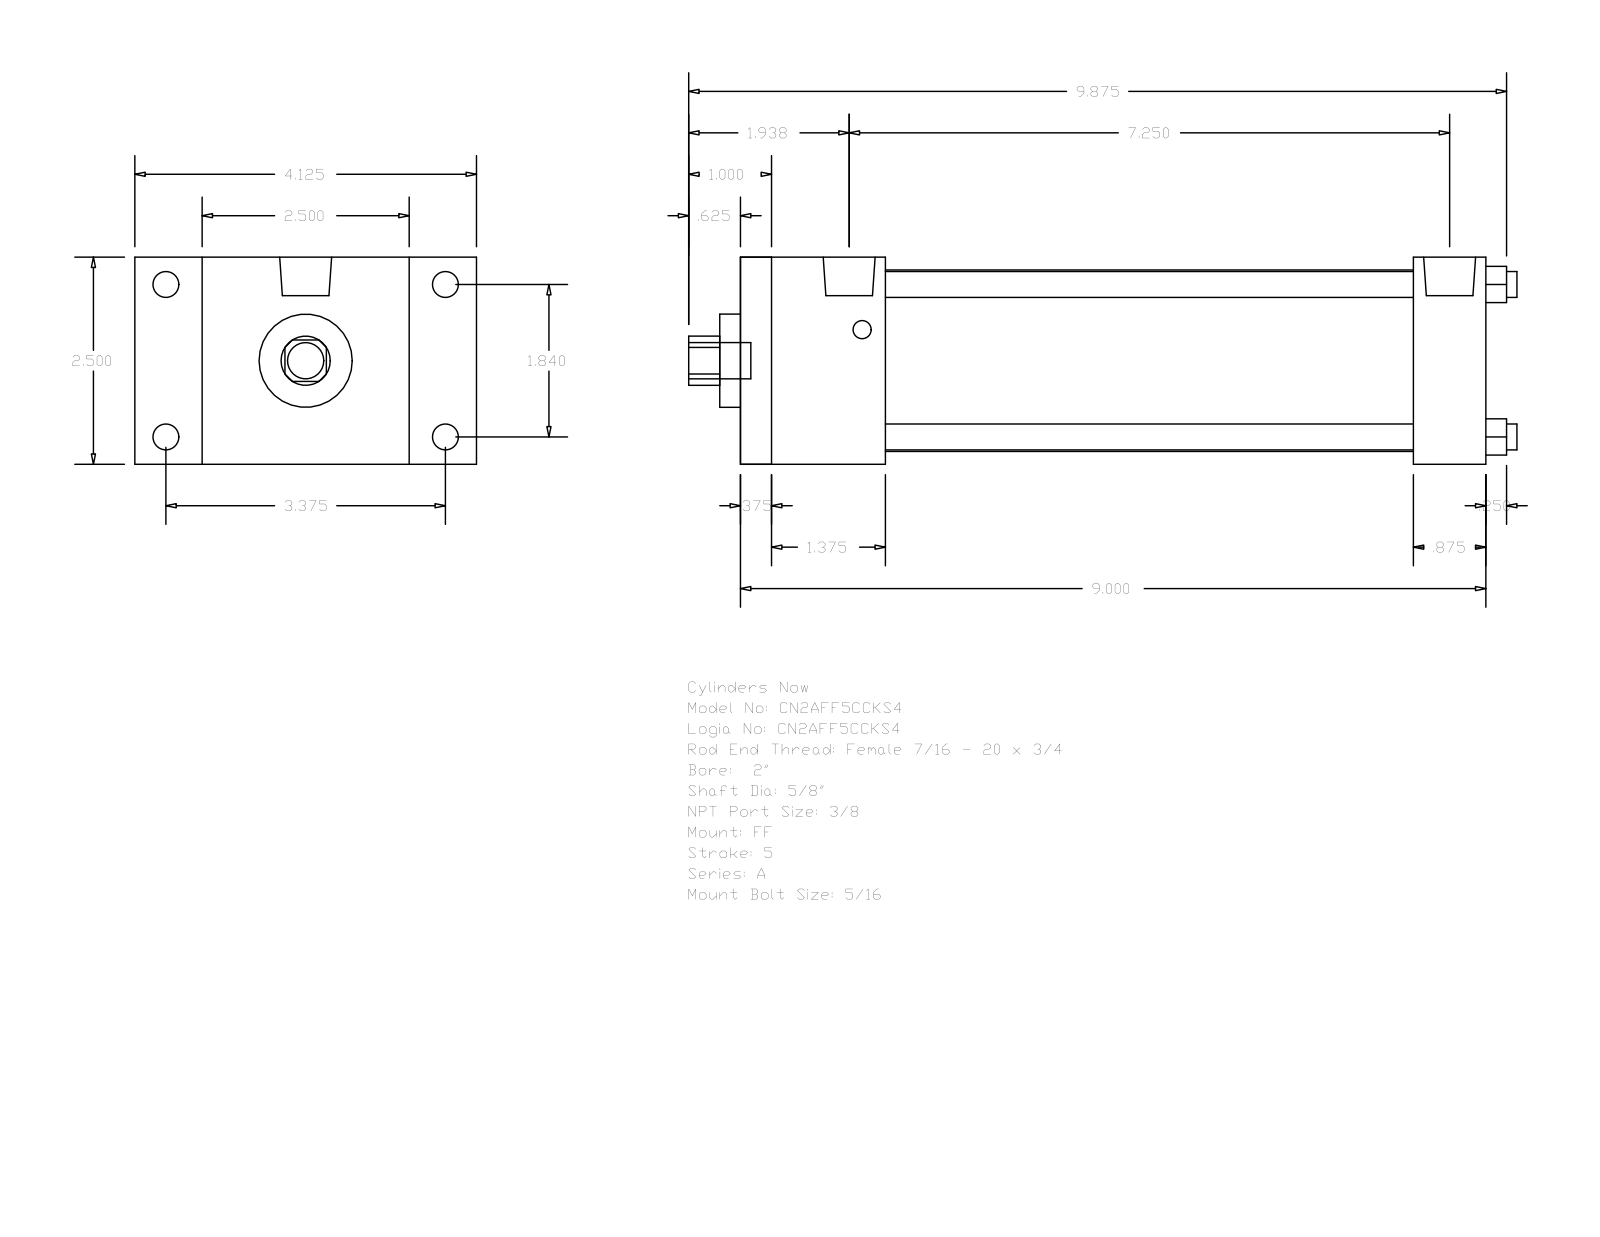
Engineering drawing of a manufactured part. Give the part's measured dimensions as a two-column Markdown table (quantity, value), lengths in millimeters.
| quantity | value |
| --- | --- |
| part name | A_FF__0200_0.625 |
| STEP written by | GSSL Pune (CONFIG_CONTROL_DESIGN) |
| units | millimeters |
| bodies | 0 solids, 92 faces (64 planar, 28 cylindrical, 0 other) |
| overall size | 254 × 104.78 × 63.5 |
| round holes (diameter × count) | 7.94 × 4, 15.88 × 1, 28.57 × 1, 55.63 × 1 |
| round bosses / shafts (diameter × count) | 7.94 × 4, 5.56 × 4, 15.93 × 2, 11.11 × 1 |
| partial cylindrical surfaces (radius × count) | 7.54 × 1 |
| main face-to-face distances | 63.5, 228.59, 9.52, 219.07, 44.45, 206.37, 34.93, 196.85, 161.92, 184.14 |
| hole center spacings | 33.05, 46.74, 66.1 |
